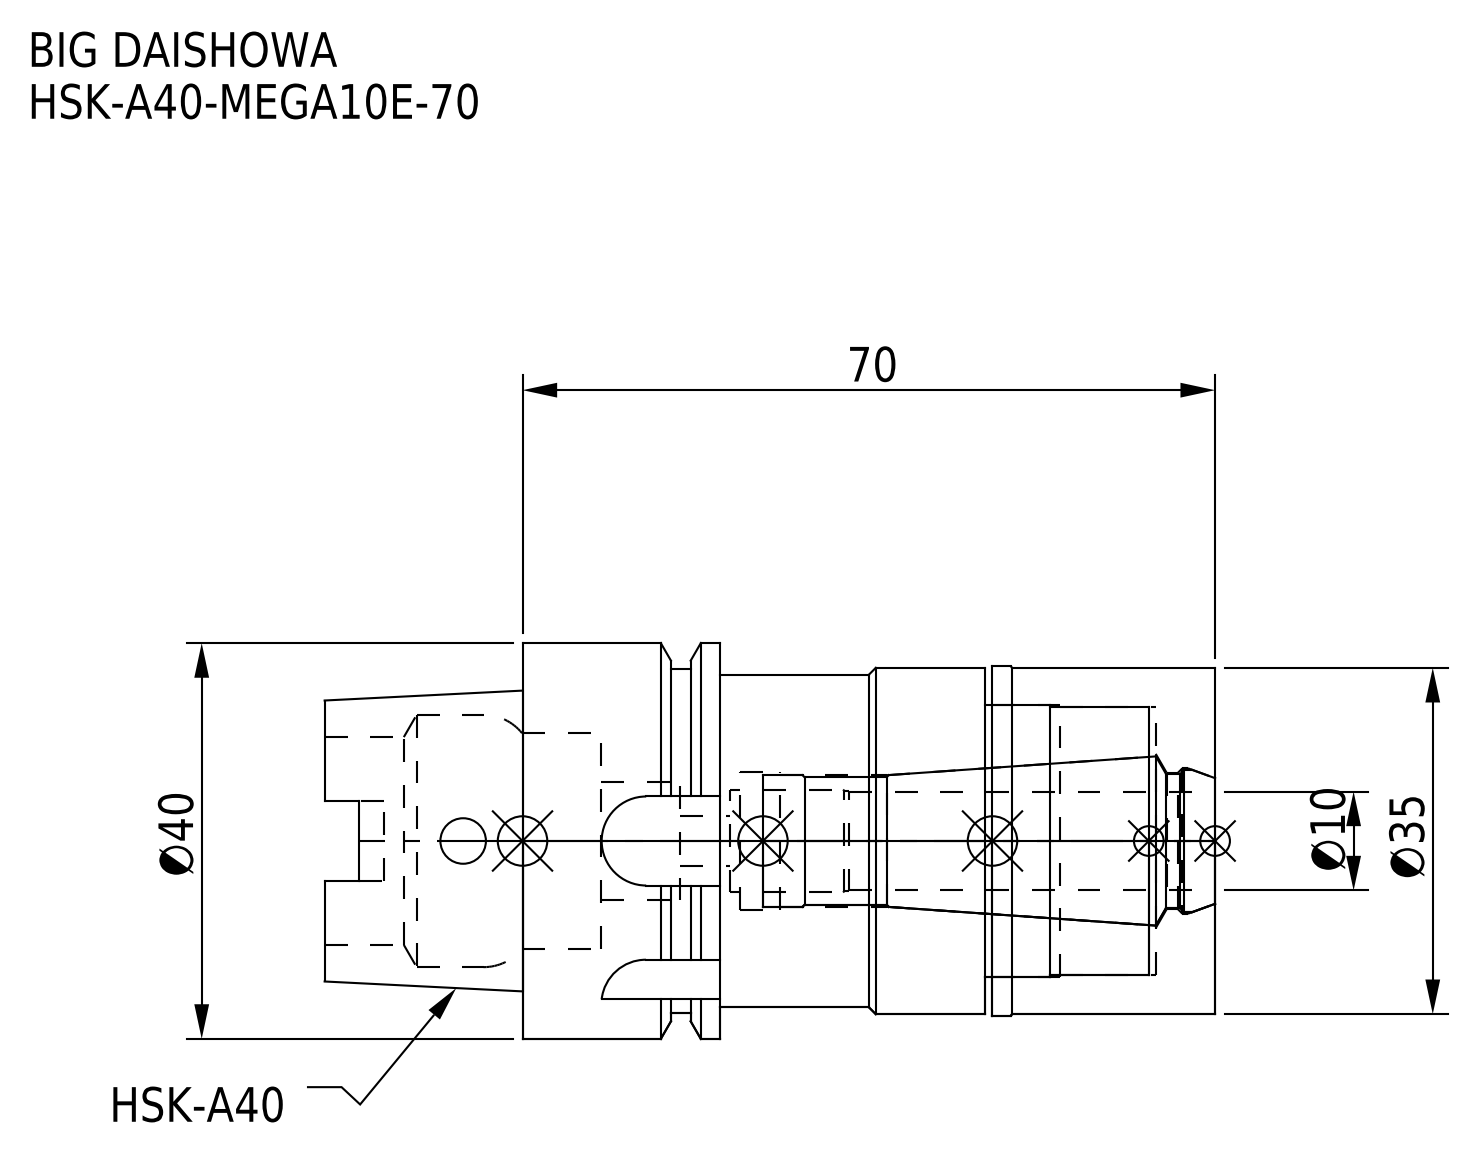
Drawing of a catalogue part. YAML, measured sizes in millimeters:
part_name: "HSK-A40-MEGA10E-70-100-FreeParts; HA40ME10070-100_ASM.stp; HSK-A40-MEGA10E-70_1.stp; HSK-A40-MEGA10E-70-100.stp (+3 more)"
step_written_by: "SolidWorks 2019 (CONFIG_CONTROL_DESIGN)"
units: millimeters
bodies: {solids: 2, faces: 129, planar: 45, cylindrical: 58, other: 26}
overall_size: [90, 40, 40]
volume: 62654
surface_area: 21608
round_holes:
  - {diameter: 4.6, count: 1}
  - {diameter: 5, count: 1}
  - {diameter: 10.4, count: 1}
  - {diameter: 12, count: 1}
  - {diameter: 13.3, count: 1}
  - {diameter: 13.8, count: 1}
  - {diameter: 13.9, count: 1}
  - {diameter: 14.7, count: 1}
  - {diameter: 21, count: 1}
  - {diameter: 21.8, count: 1}
  - {diameter: 25.5, count: 1}
  - {diameter: 27, count: 1}
round_bosses_or_shafts:
  - {diameter: 40, count: 1}
  - {diameter: 35.3, count: 1}
  - {diameter: 35, count: 1}
  - {diameter: 34.8, count: 1}
  - {diameter: 33.6, count: 1}
partial_cylinders:
  - {radius: 1.88, count: 4}
  - {radius: 4.5, count: 4}
face_to_face_distances: [70, 20, 6, 22.5, 47.5, 16.5, 23.3, 0.8, 46.7, 64]
